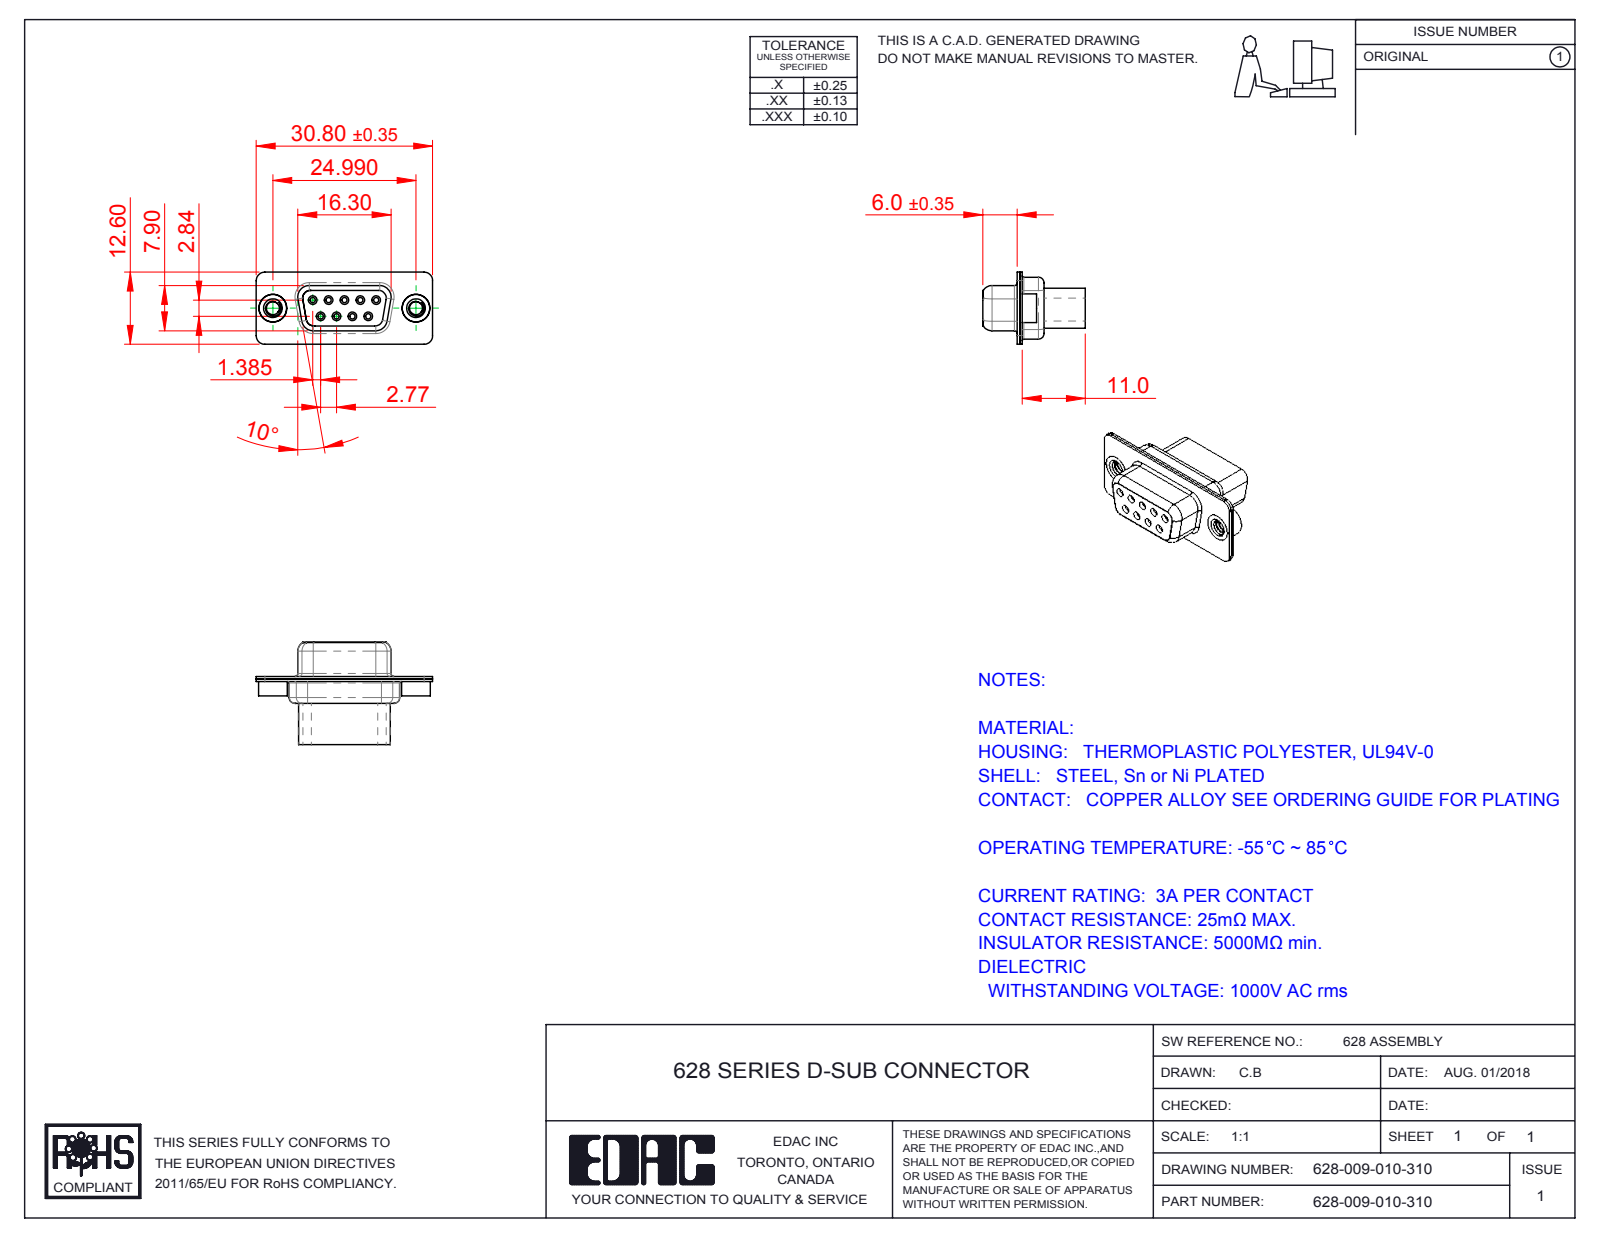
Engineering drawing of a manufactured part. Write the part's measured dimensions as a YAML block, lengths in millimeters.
part_name: "628 4-40 Threaded Rivet; 628 Shell Rear_09 Contacts; 628 Shell Front_09 Contacts; 628-009-010-310 (+1 more)"
step_written_by: "SolidWorks 2016 (CONFIG_CONTROL_DESIGN)"
units: millimeters
bodies: {solids: 5, faces: 392, planar: 94, cylindrical: 207, other: 91}
overall_size: [30.8, 17.9, 12.6]
volume: 2142
surface_area: 4084
round_holes:
  - {diameter: 0.9, count: 9}
  - {diameter: 1.5, count: 9}
  - {diameter: 2, count: 9}
  - {diameter: 1.7, count: 5}
  - {diameter: 1.6, count: 4}
  - {diameter: 2.26, count: 2}
  - {diameter: 4, count: 2}
  - {diameter: 4.05, count: 2}
  - {diameter: 4.85, count: 2}
round_bosses_or_shafts:
  - {diameter: 5, count: 2}
  - {diameter: 4.95, count: 2}
  - {diameter: 4.8, count: 2}
partial_cylinders:
  - {radius: 1.5, count: 17}
  - {radius: 2, count: 12}
  - {radius: 1.35, count: 6}
  - {radius: 0.25, count: 4}
  - {radius: 0.5, count: 4}
  - {radius: 0.6, count: 4}
  - {radius: 0.65, count: 4}
  - {radius: 0.95, count: 4}
face_to_face_distances: [0.45, 0.4, 0.9, 6.6, 1.9, 8.5, 1.4, 7, 0.5, 0.85]
hole_center_spacings: [3.16, 2.77, 5.54, 5.03, 5.04, 8.31, 7.48, 7.49]
